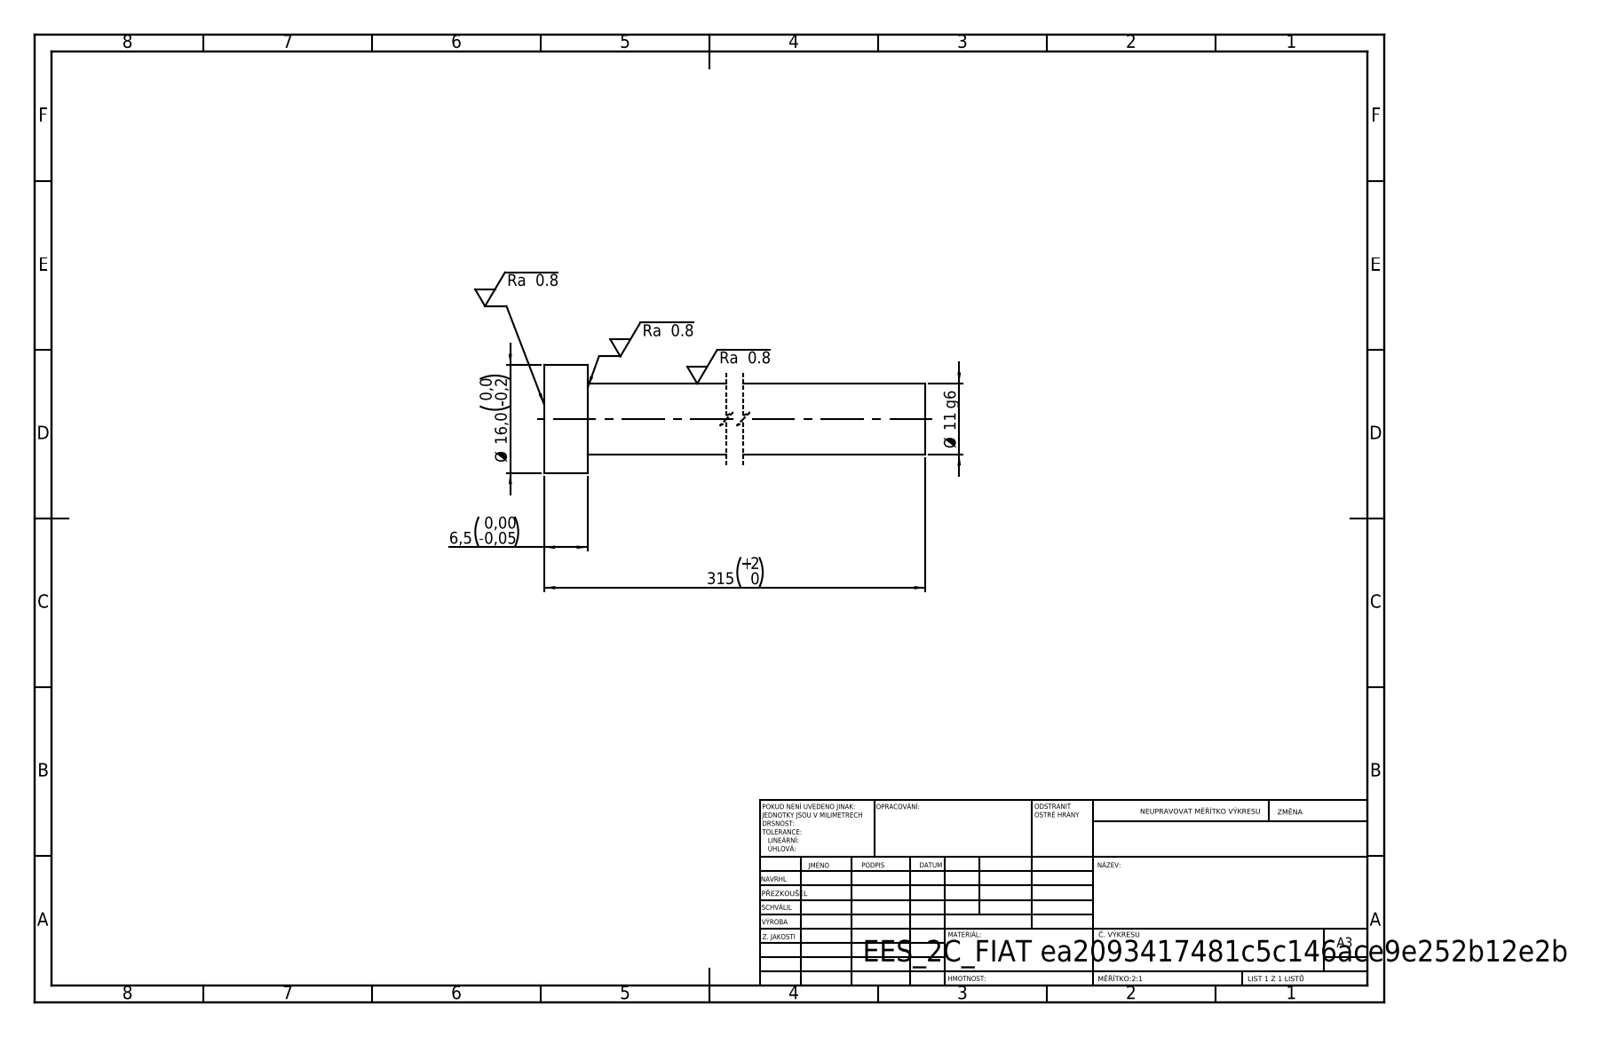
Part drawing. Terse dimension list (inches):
written by: SolidWorks 2019 (CONFIG_CONTROL_DESIGN)
unit: in
bodies: 1 solid, 7 faces (3 planar, 4 cylindrical, 0 other)
size: 12.402 × 0.63 × 0.63
volume: 1.71 in³; area: 16.9 in²
bosses: 1× ⌀0.63, 1× ⌀0.413
face distances: 0.256, 12.402, 12.146
